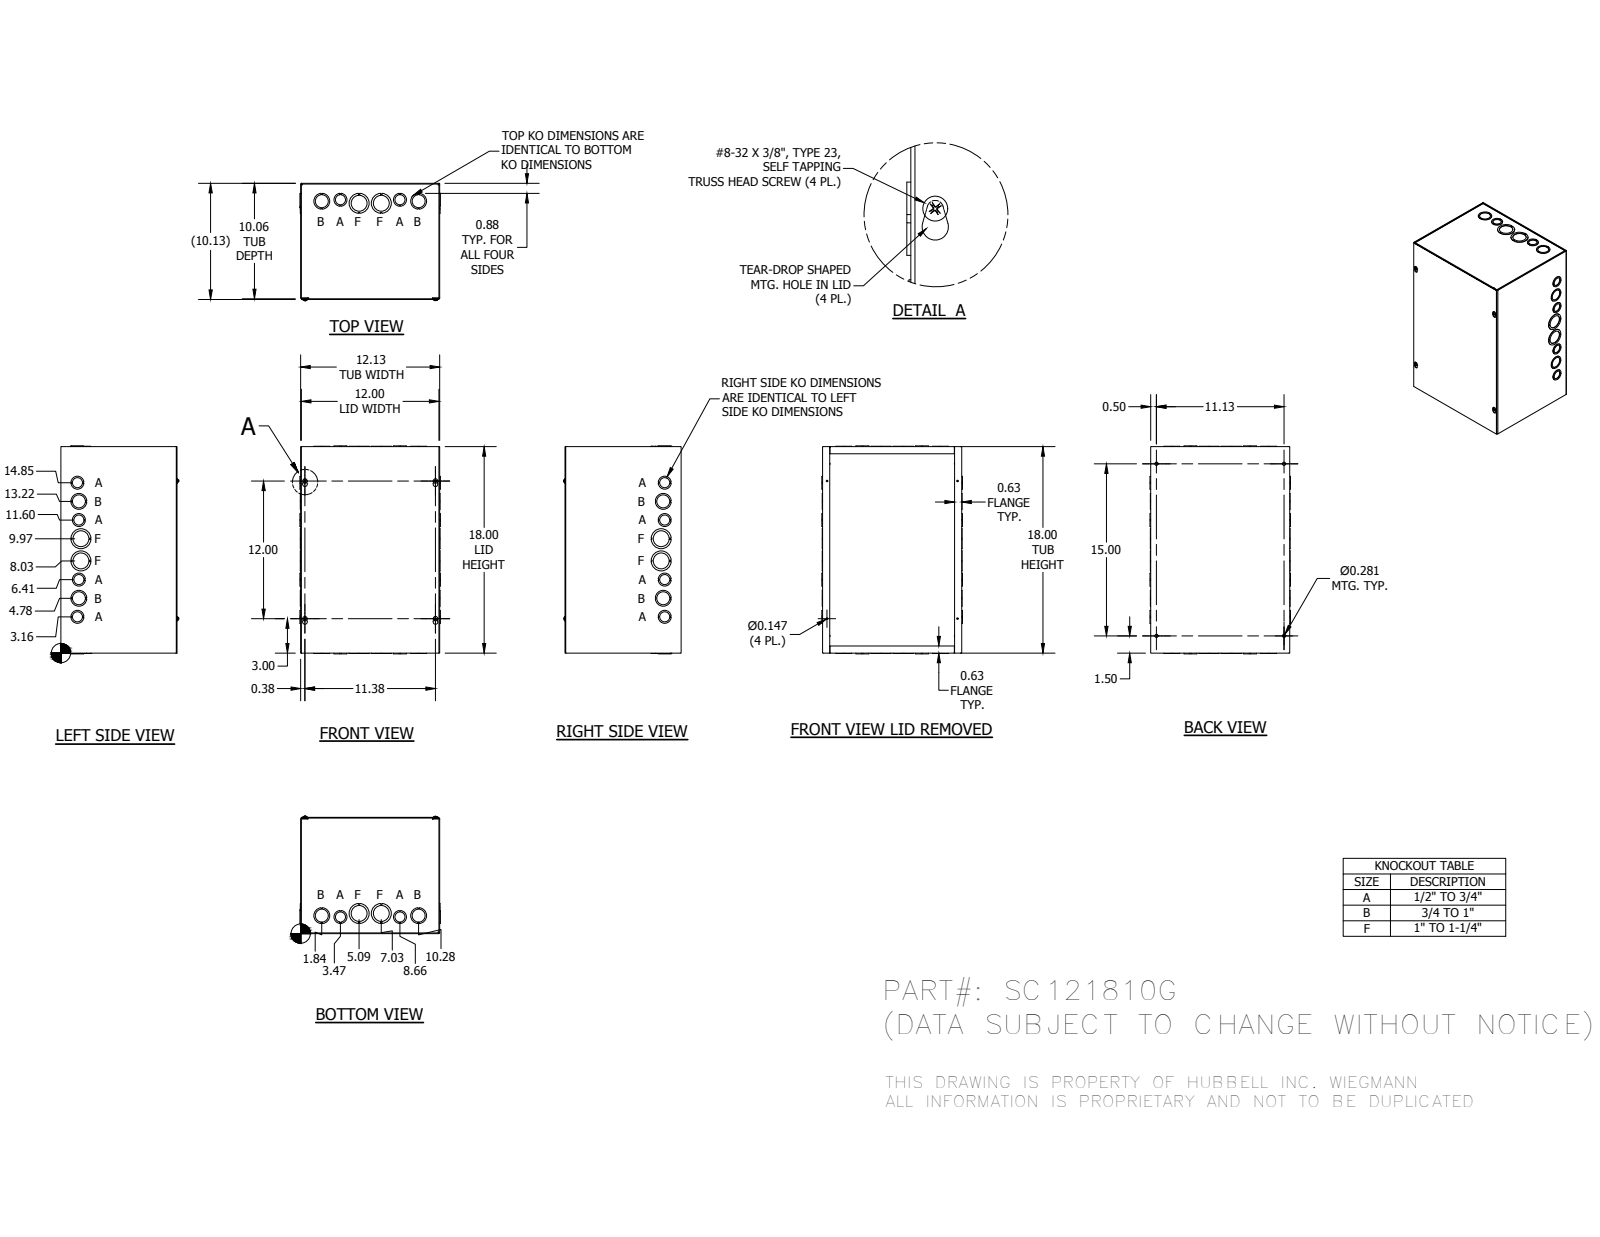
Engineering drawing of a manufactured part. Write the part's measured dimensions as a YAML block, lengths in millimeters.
part_name: "SC121810GBLR; SC1210GTB; SC1218GLPA; 34056 (+1 more)"
step_written_by: "Autodesk Inventor 2014 (AUTOMOTIVE_DESIGN)"
units: millimeters
bodies: {solids: 29, faces: 1055, planar: 771, cylindrical: 216, other: 68}
overall_size: [460.38, 311.15, 259.72]
round_holes:
  - {diameter: 28.57, count: 12}
  - {diameter: 22.22, count: 8}
  - {diameter: 34.92, count: 8}
  - {diameter: 3.73, count: 4}
  - {diameter: 7.14, count: 4}
  - {diameter: 44.45, count: 4}
round_bosses_or_shafts:
  - {diameter: 9.75, count: 4}
  - {diameter: 4.17, count: 4}
partial_cylinders:
  - {radius: 0.4, count: 12}
  - {radius: 1.98, count: 12}
  - {radius: 3.17, count: 4}
  - {radius: 5.16, count: 4}
face_to_face_distances: [1.59, 306.39, 254, 1.58, 455.61, 255.59, 255.58, 257.17, 304.8, 307.98]
hole_center_spacings: [38.23, 41.4, 42.03, 82.69, 90.9, 131.92, 173.13, 288.28]
